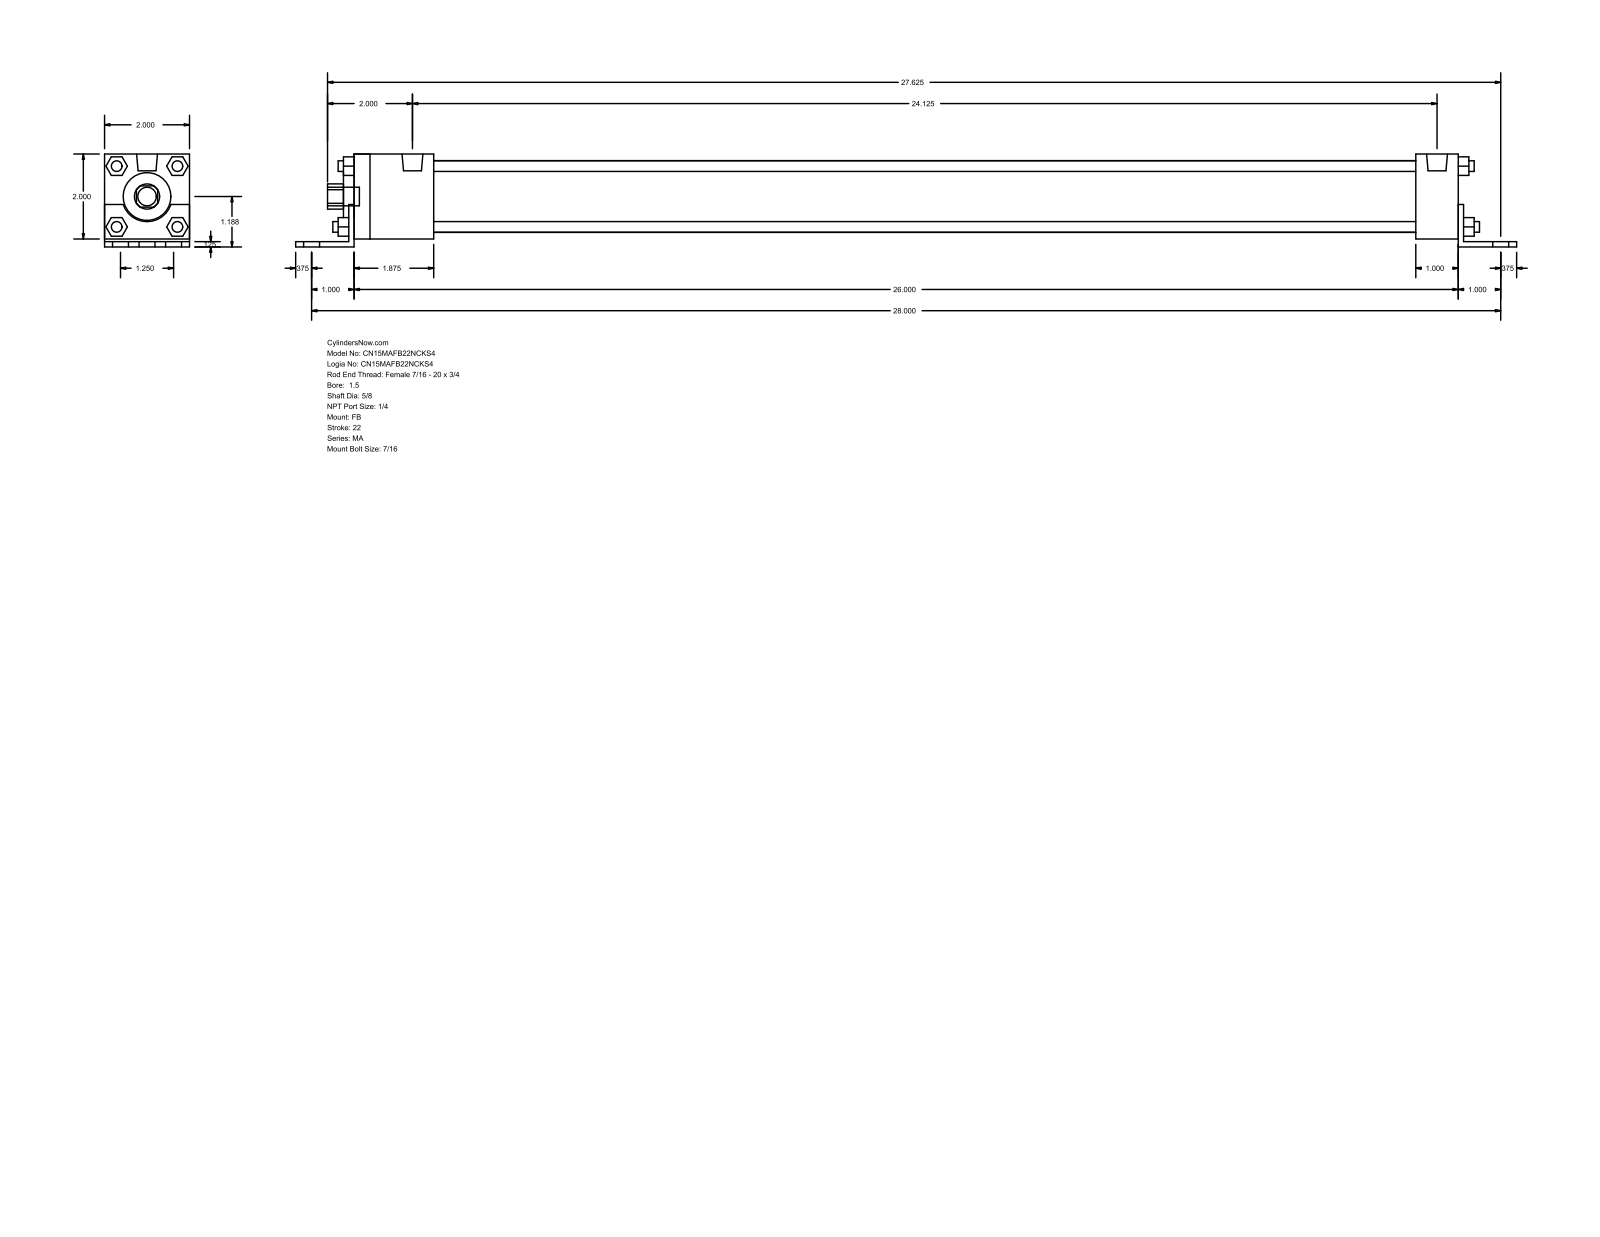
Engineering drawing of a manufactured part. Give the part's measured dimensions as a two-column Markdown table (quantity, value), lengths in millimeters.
| quantity | value |
| --- | --- |
| part name | MA_FB__0150_0.625 |
| STEP written by | GSSL Pune (CONFIG_CONTROL_DESIGN) |
| units | millimeters |
| bodies | 0 solids, 140 faces (105 planar, 35 cylindrical, 0 other) |
| overall size | 730.25 × 55.56 × 50.8 |
| round holes (diameter × count) | 15.88 × 1, 28.57 × 1, 42.93 × 1 |
| round bosses / shafts (diameter × count) | 11.11 × 7, 7.94 × 4, 6.35 × 4, 12.49 × 2 |
| partial cylindrical surfaces (radius × count) | 7.54 × 1, 15.05 × 1 |
| main face-to-face distances | 50.8, 3.17, 4.76, 55.56, 1.59, 52.39, 3.18, 663.57, 6.35, 669.92 |
